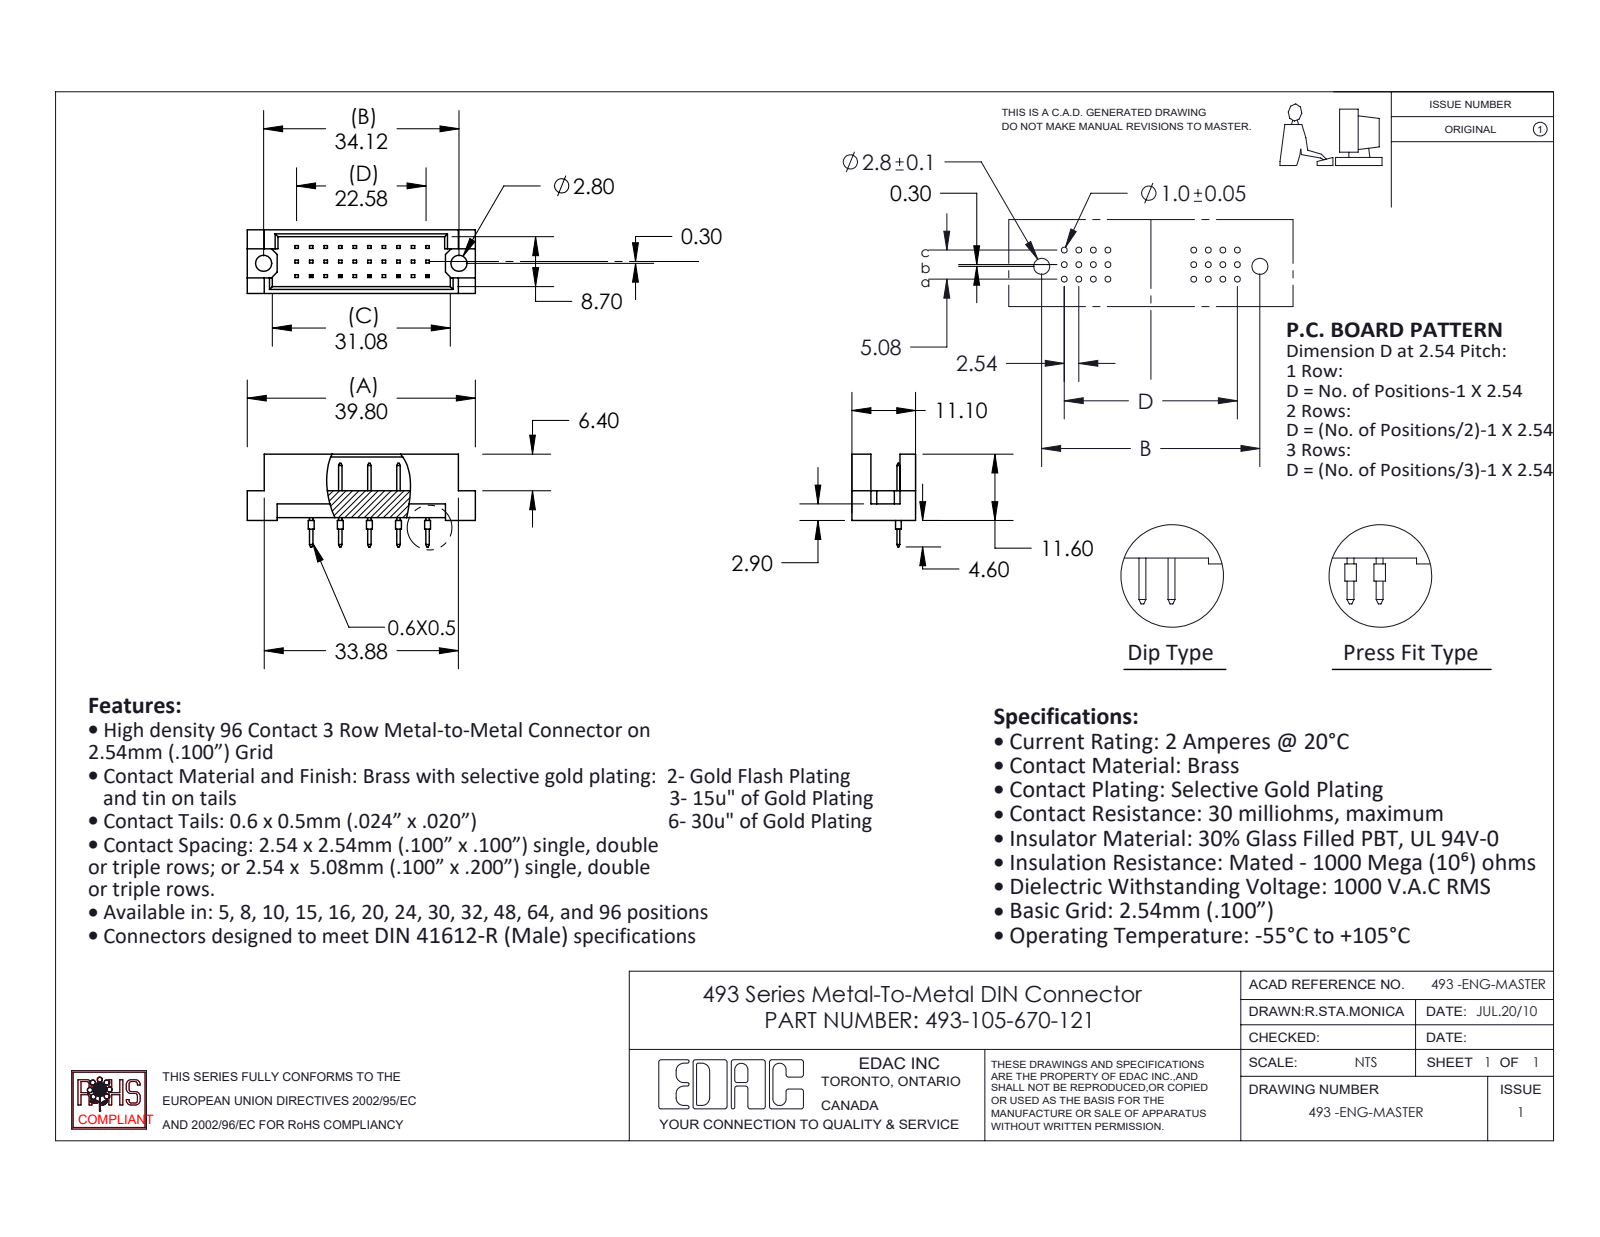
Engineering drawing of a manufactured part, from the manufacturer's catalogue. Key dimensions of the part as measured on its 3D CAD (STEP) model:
Part name (STEP PRODUCT): 493-105-670-121; 493-290_70; 493 Part_30
STEP written by: SolidWorks 2020 (CONFIG_CONTROL_DESIGN)
Units: millimetres
Bodies: 6 solids, 282 faces (268 planar, 14 cylindrical, 0 other)
Overall size (bounding box): 39.8 × 16.2 × 11.1
Volume: 2 398 mm³ · Surface area: 2 908 mm²
Round holes (diameter × count): ⌀2.8 ×2
Round bosses / shafts (diameter × count): ⌀1 ×5
Main face-to-face distances: 1.2, 9.9, 11.1, 8.7, 4.7, 0.5, 5.08, 2.4, 2.54, 2.3
Hole centre spacings: 34.12
